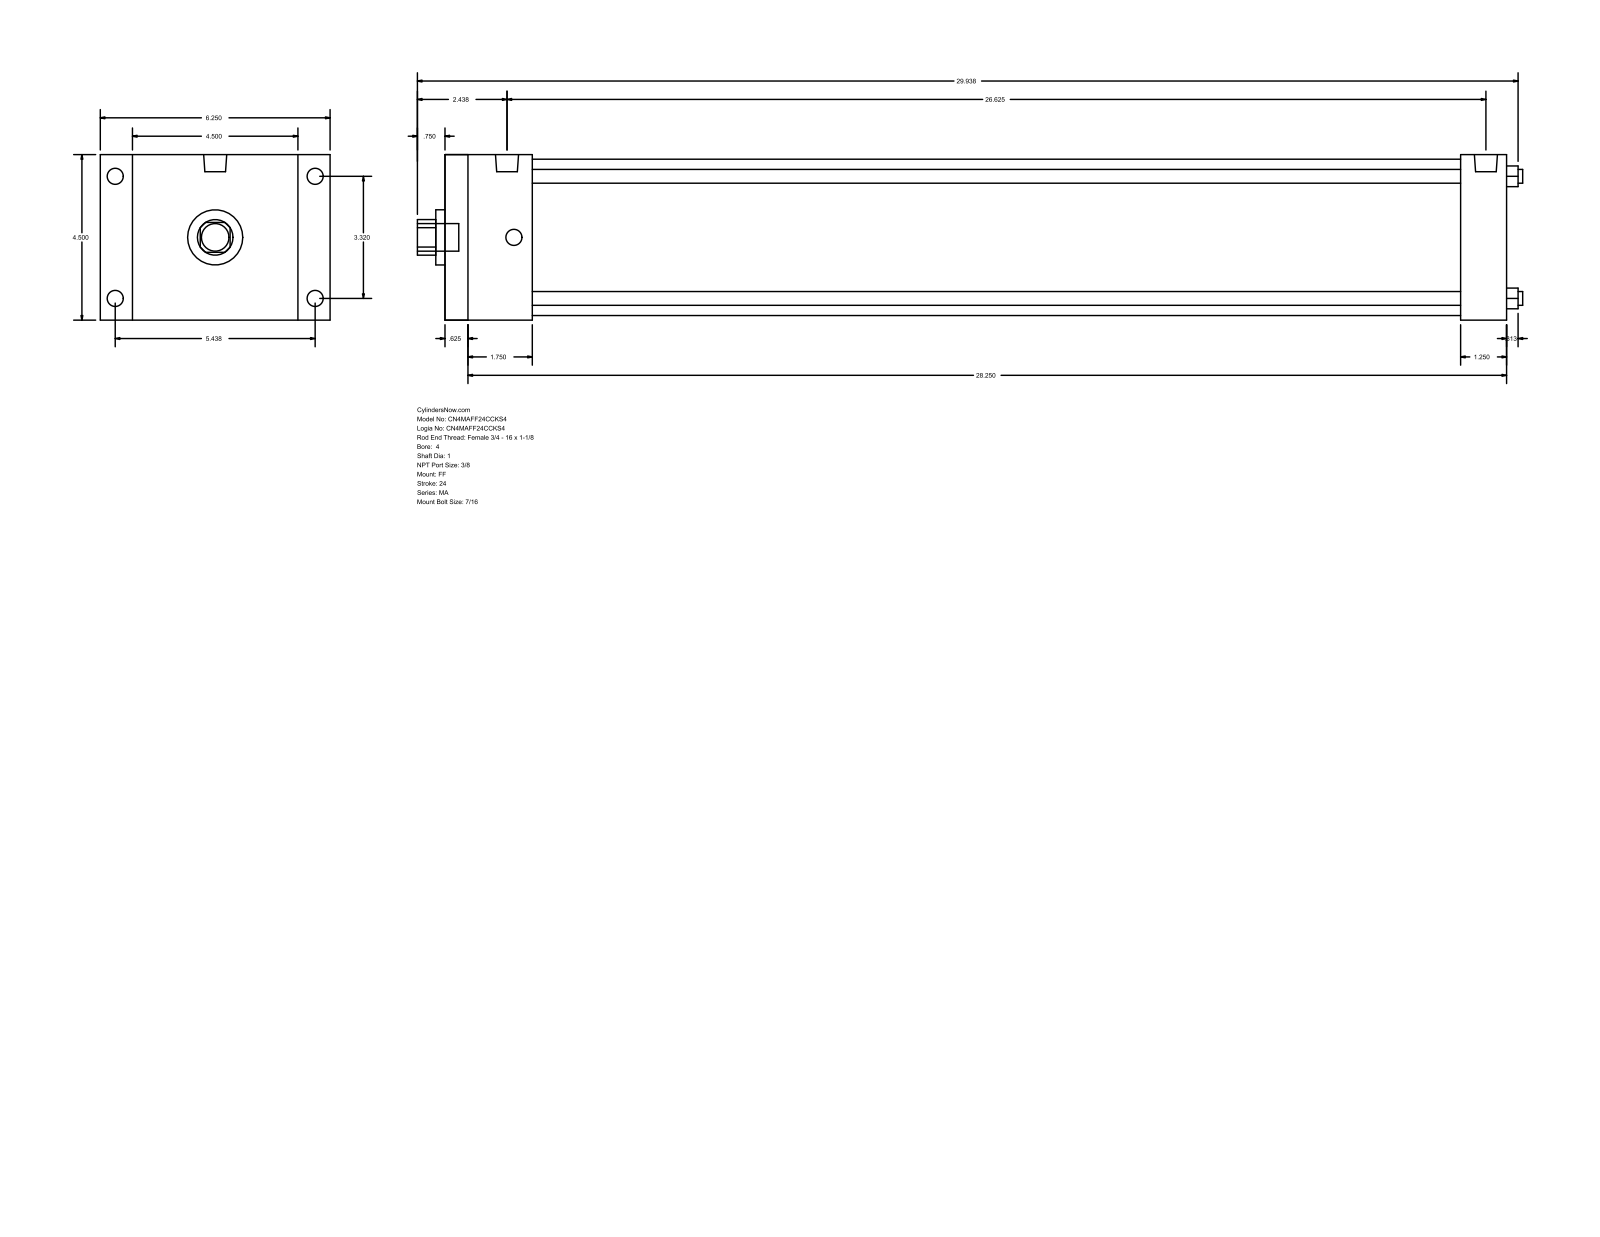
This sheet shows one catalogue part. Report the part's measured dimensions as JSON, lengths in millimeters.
{"part_name": "MA_FF__0400_1", "step_written_by": "GSSL Pune (CONFIG_CONTROL_DESIGN)", "units": "millimeters", "bodies": {"solids": 0, "faces": 92, "planar": 64, "cylindrical": 28, "other": 0}, "overall_size": [763.59, 158.75, 114.3], "round_holes": [[9.53, 4], [25.4, 1], [38.1, 1], [107.95, 1]], "round_bosses_or_shafts": [[11.11, 8], [15.93, 2], [19.05, 1]], "partial_cylinders_radius": [[12.29, 1]], "face_to_face_distances": [114.3, 733.43, 15.87, 717.56, 22.23, 136.53, 701.68, 685.81, 31.75, 60.33], "hole_center_spacings": [59.62, 84.32, 119.25]}
